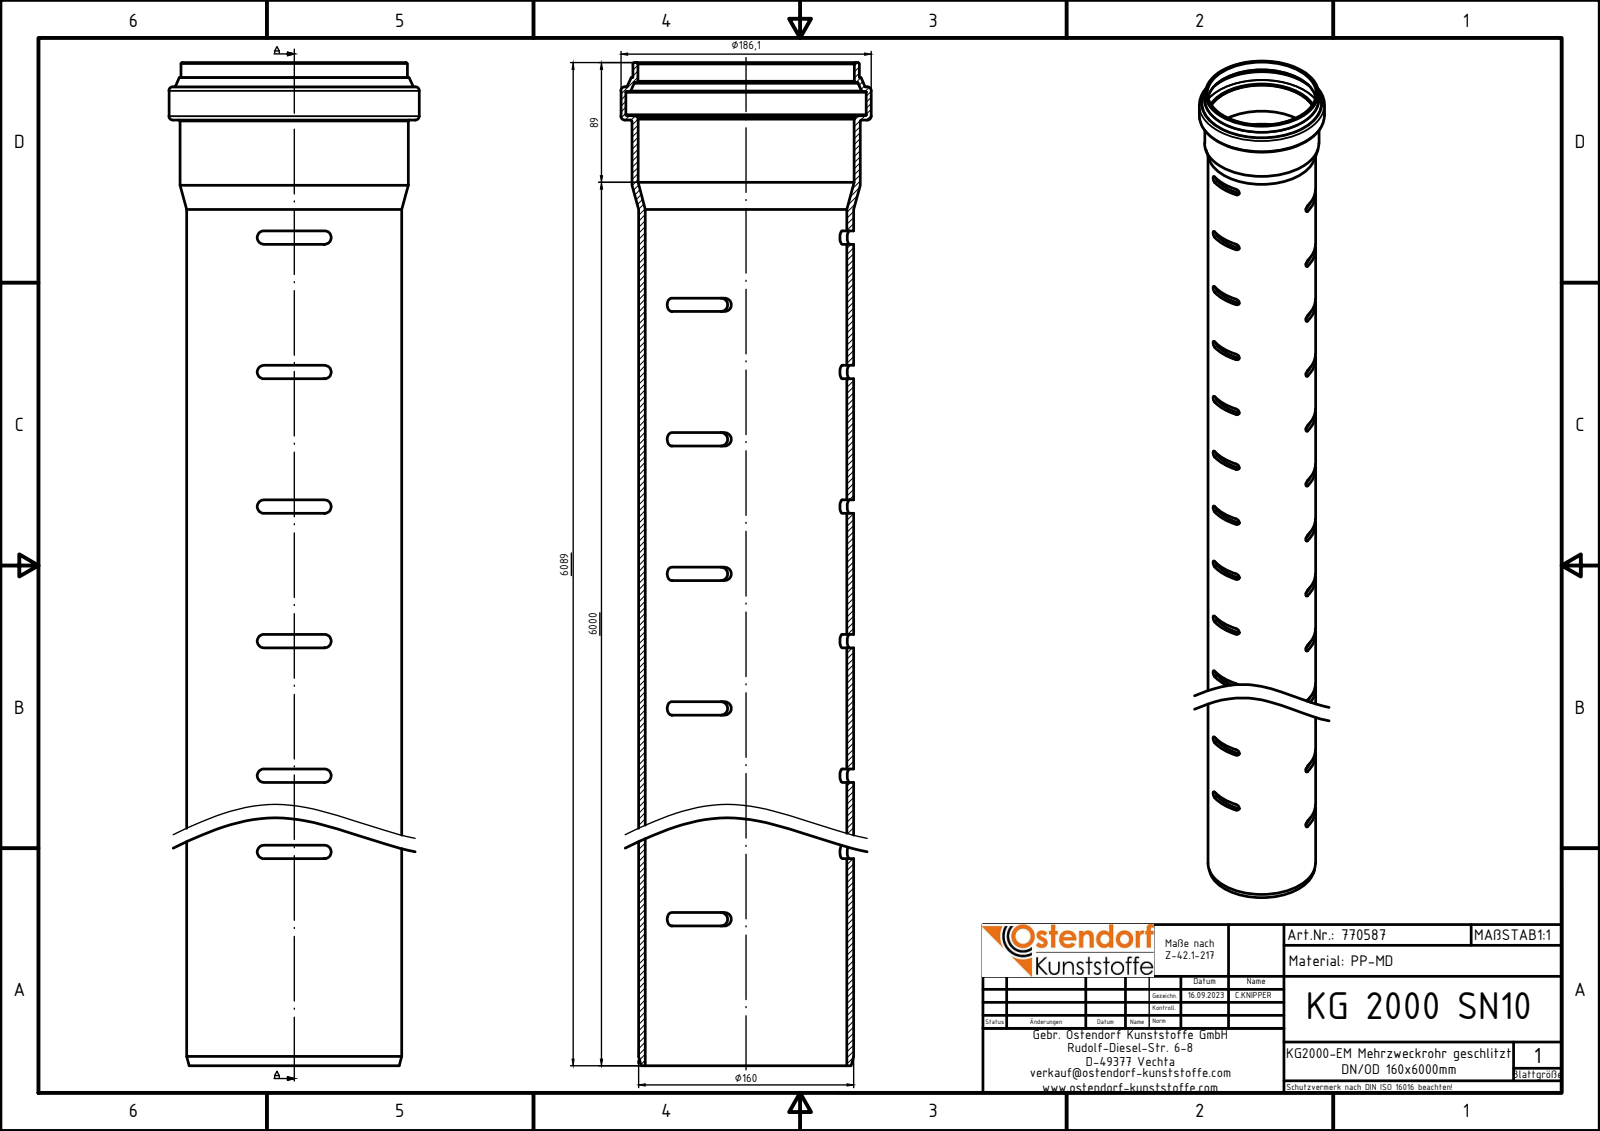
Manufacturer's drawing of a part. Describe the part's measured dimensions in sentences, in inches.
The part is named "770587z". Its 3-D file was written by "Autodesk Inventor 2024 (AUTOMOTIVE_DESIGN)". It is 1 solid with 509 faces: 242 planar, 245 cylindrical and 22 other. Overall it measures 239.724 by 7.327 by 7.327 inches. Its volume is 897.7 cubic inches and its surface area 9 147 square inches. Round holes: 1 of diameter 5.9, 1 of diameter 6.323, 1 of diameter 6.339, 1 of diameter 7.035. Round bosses or shafts: 1 of diameter 7.327, 1 of diameter 6.677, 1 of diameter 6.63, 1 of diameter 6.299. Partial cylindrical surfaces (rounded edges, fillets, slot ends): 236 of radius 0.197. The main face-to-face distances are 3.937, 7.874, 11.811, 15.748, 19.685, 23.622, 27.559, 31.496, 238.043, 35.433.
